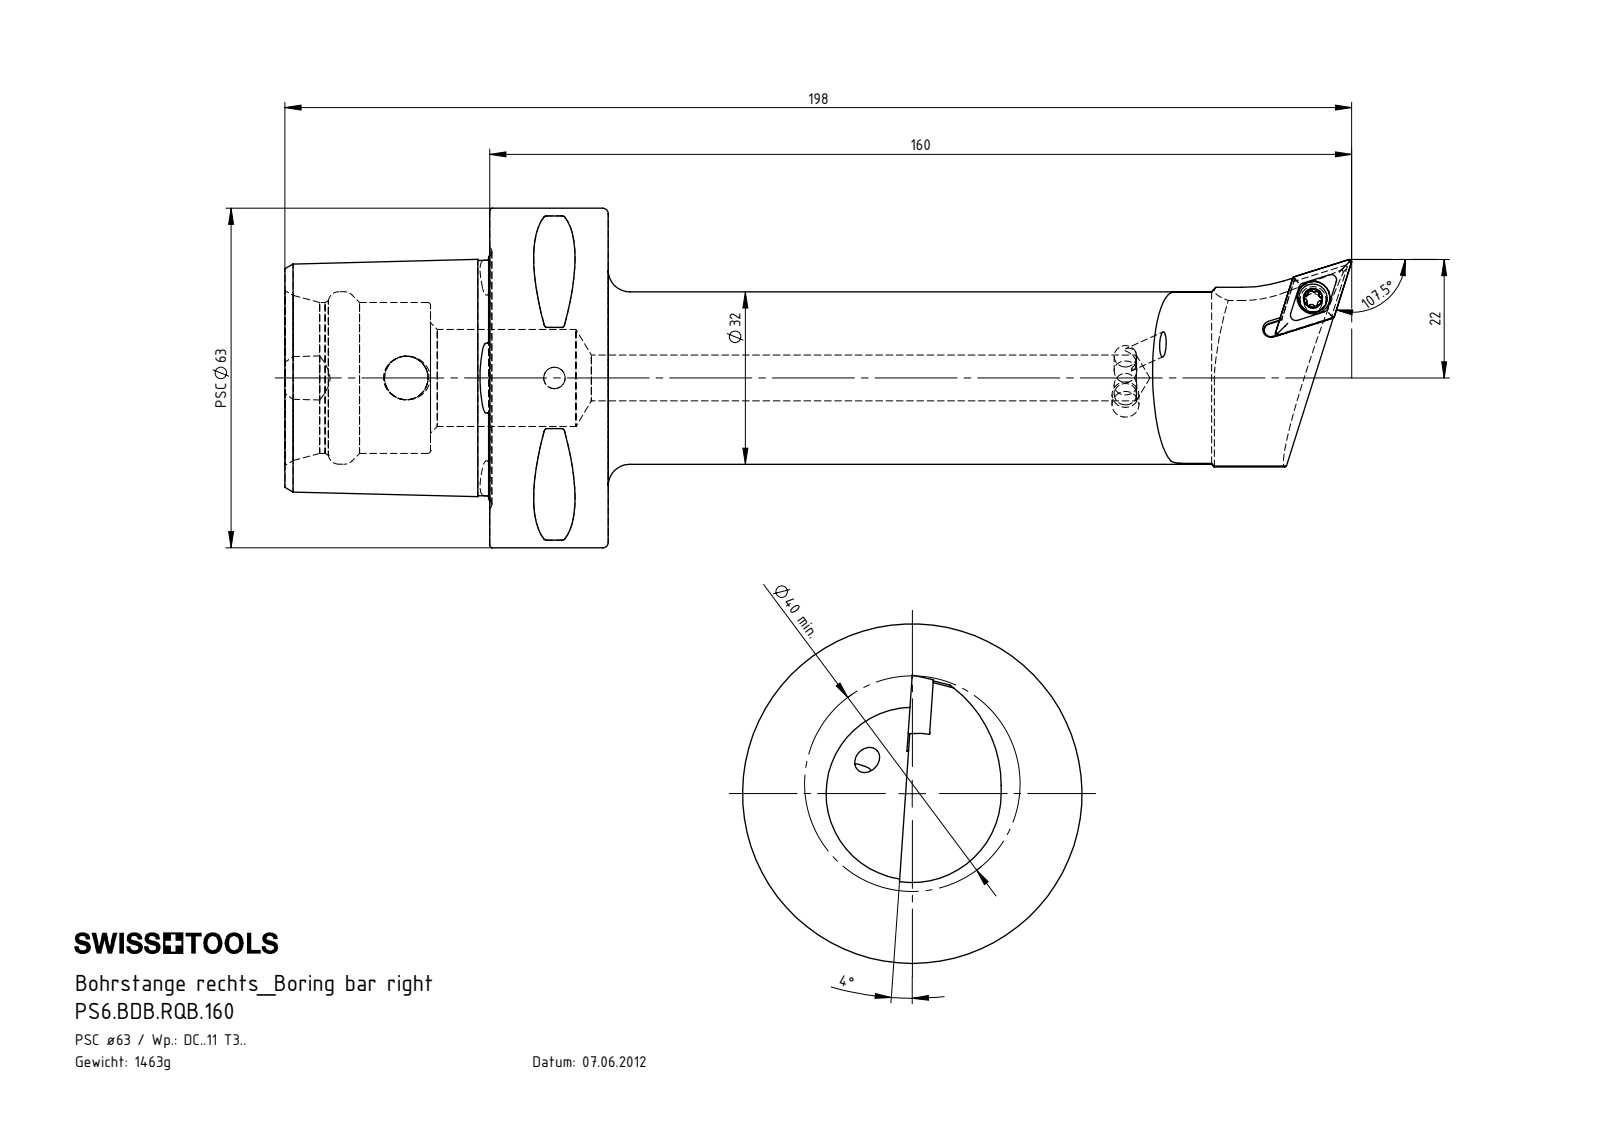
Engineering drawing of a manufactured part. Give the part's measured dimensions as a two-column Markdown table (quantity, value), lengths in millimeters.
| quantity | value |
| --- | --- |
| part name | KVT_MB_600_050; PS6-BDB.RQB.160_A; PS6.BDB.RQB.160; DCMT11T304 (+1 more) |
| STEP written by | SolidWorks 2017 (AUTOMOTIVE_DESIGN) |
| units | millimeters |
| bodies | 5 solids, 284 faces (53 planar, 73 cylindrical, 158 other) |
| overall size | 198 × 63 × 63 |
| volume | 186 748 mm³ |
| surface area | 36 586 mm² |
| round holes (diameter × count) | 4 × 2, 4.2 × 2, 3.3 × 1, 4.4 × 1, 6.1 × 1, 8.1 × 1, 8.5 × 1, 18 × 1, 28 × 1, 32 × 1 |
| round bosses / shafts (diameter × count) | 63 × 1, 5.25 × 1, 5 × 1, 4 × 1 |
| partial cylindrical surfaces (radius × count) | 0.5 × 8, 0.34 × 6, 0.59 × 6, 1.25 × 1, 3 × 1, 6 × 1, 16.5 × 1, 23 × 1 |
| main face-to-face distances | 22, 38, 60, 24.88, 27, 11, 33, 55.8, 3.66, 37.8 |
| hole center spacings | 27.5 |
